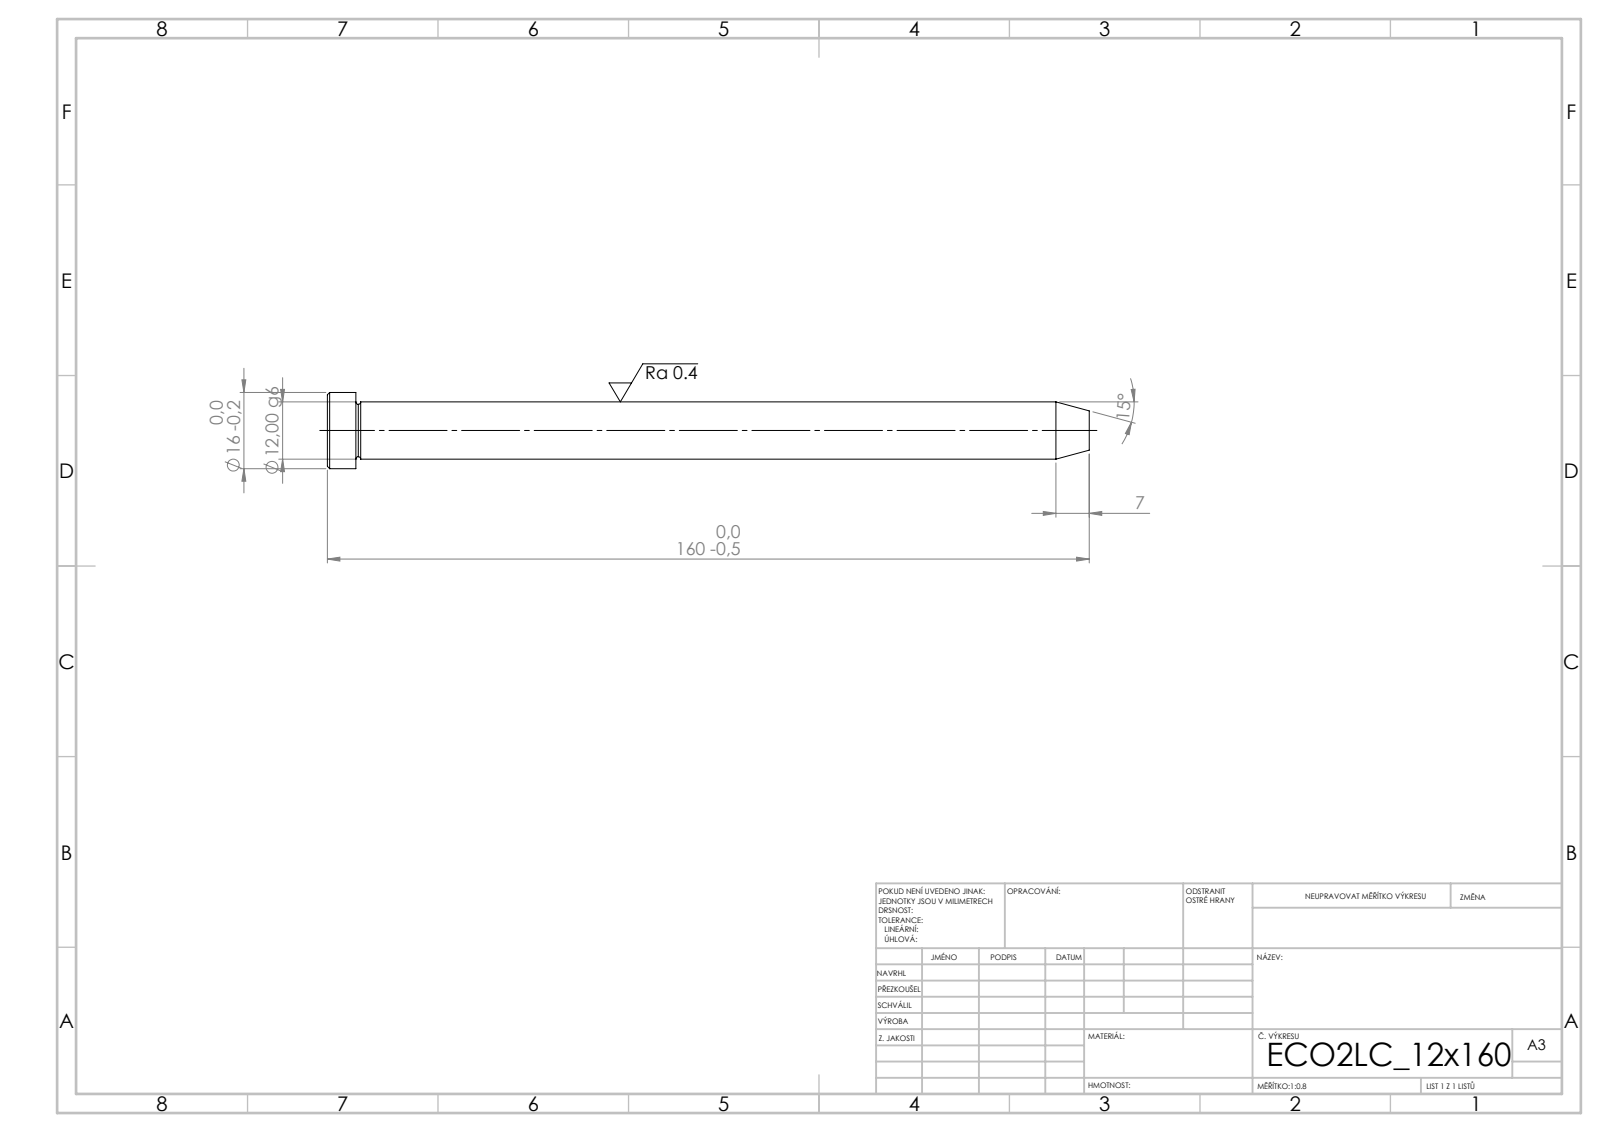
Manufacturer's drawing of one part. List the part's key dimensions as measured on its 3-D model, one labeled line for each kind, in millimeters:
STEP written by: SolidWorks 2019 (CONFIG_CONTROL_DESIGN)
Units: millimetres
Bodies: 1 solid, 15 faces (3 planar, 4 cylindrical, 8 other)
Overall size (bounding box): 160 × 16 × 16
Volume: 18 381 mm³ · Surface area: 6 420 mm²
Round bosses / shafts (diameter × count): ⌀16 ×1, ⌀12 ×1
Main face-to-face distances: 6, 154, 160
